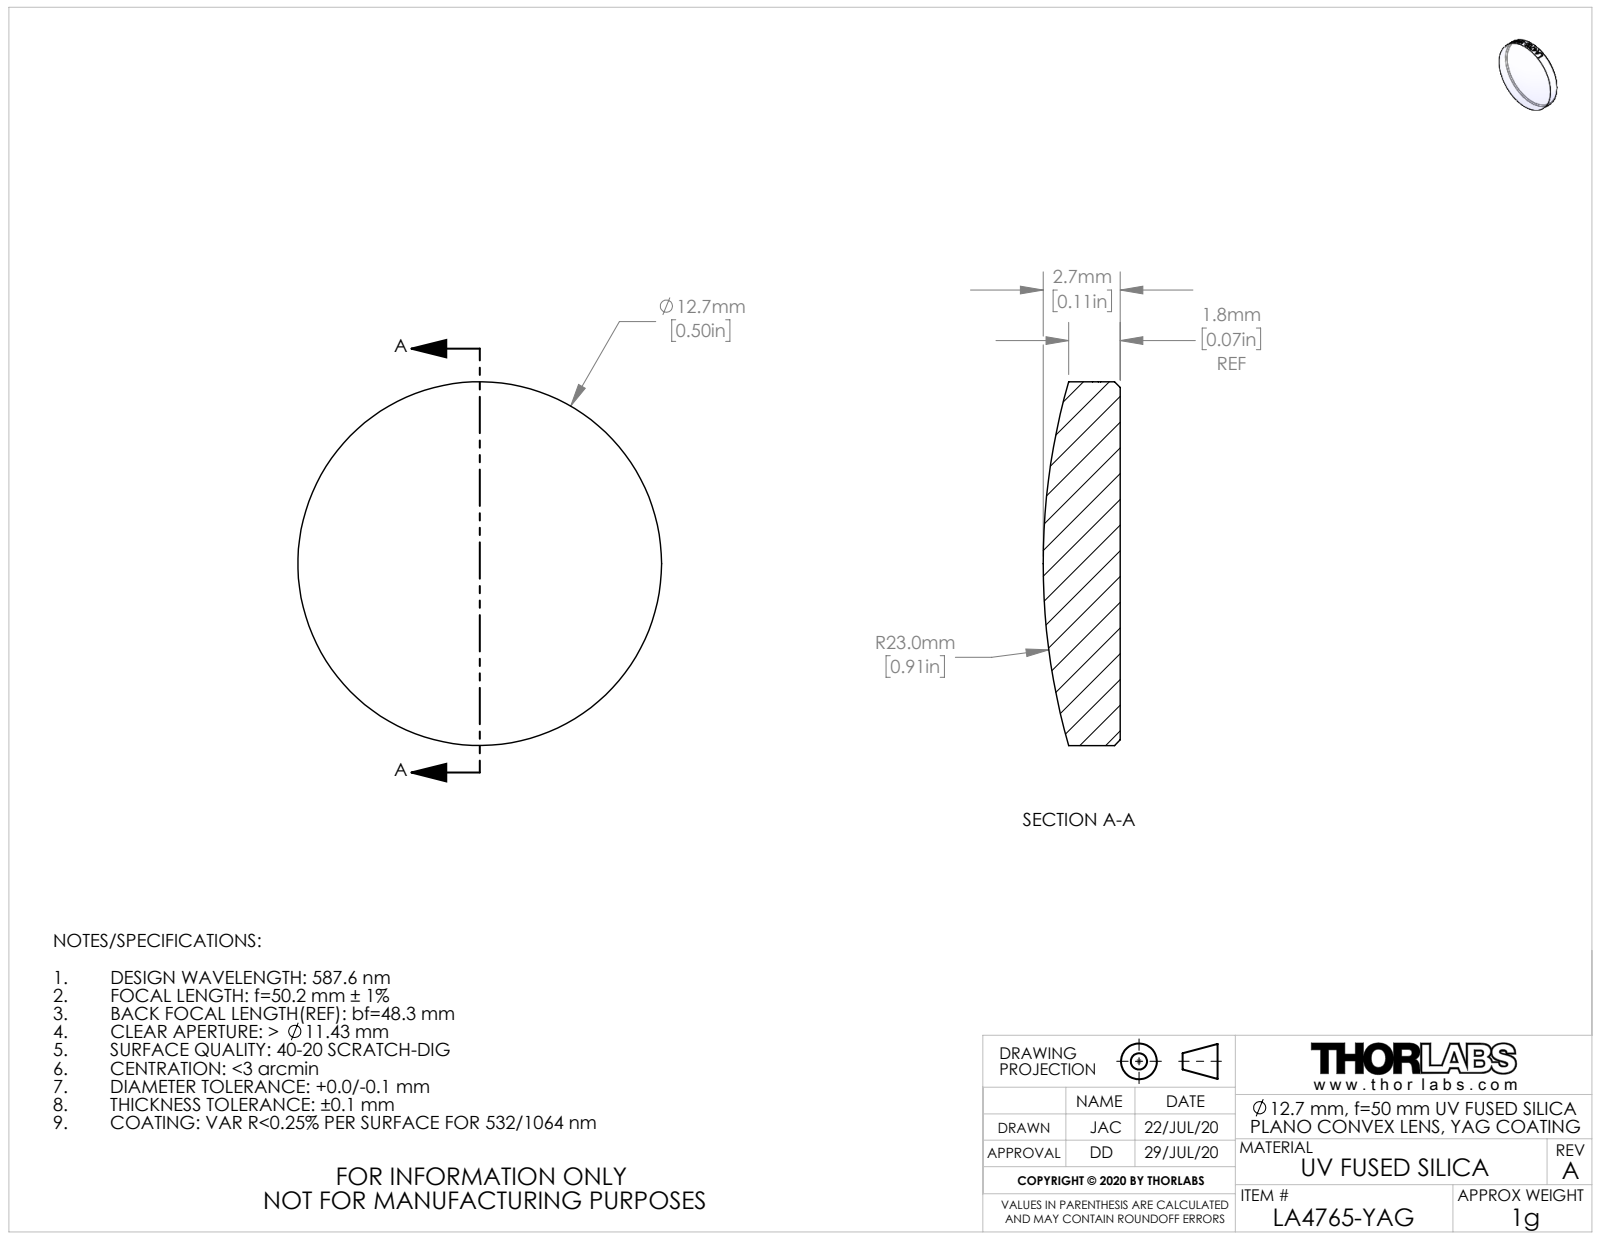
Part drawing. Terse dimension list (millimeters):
name: TTN217849-E0W
written by: SolidWorks 2018 (CONFIG_CONTROL_DESIGN)
unit: mm
bodies: 1 solid, 25 faces (1 planar, 20 cylindrical, 4 other)
size: 12.7 × 12.7 × 2.7
volume: 280 mm³; area: 323 mm²
bosses: 1× ⌀12.7
